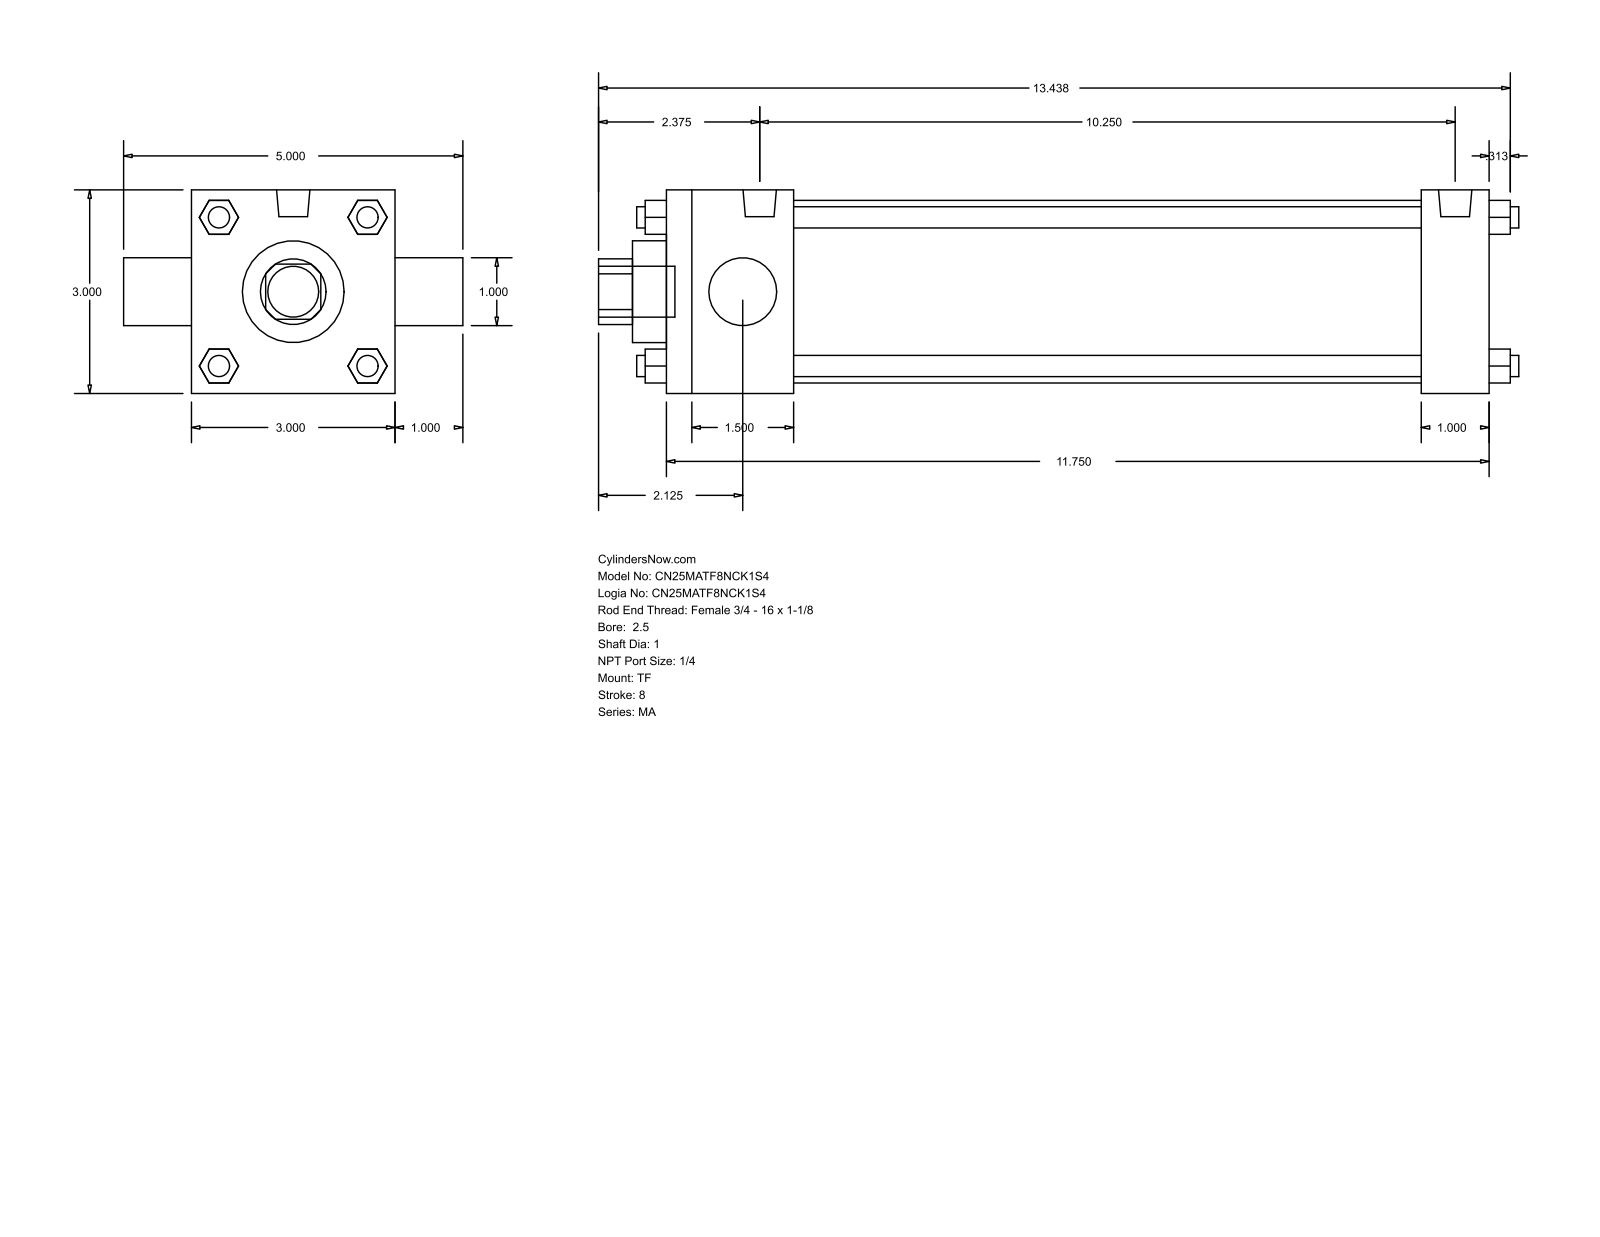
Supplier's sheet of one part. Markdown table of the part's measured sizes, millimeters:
| quantity | value |
| --- | --- |
| part name | MA_TF__0250_1 |
| STEP written by | GSSL Pune (CONFIG_CONTROL_DESIGN) |
| units | millimeters |
| bodies | 0 solids, 120 faces (92 planar, 28 cylindrical, 0 other) |
| overall size | 344.49 × 127 × 76.2 |
| round holes (diameter × count) | 25.4 × 2, 38.1 × 1, 68.33 × 1 |
| round bosses / shafts (diameter × count) | 7.94 × 7, 12.49 × 2, 19.05 × 1 |
| partial cylindrical surfaces (radius × count) | 12.29 × 1 |
| main face-to-face distances | 76.2, 307.98, 25.4, 12.7, 47.63, 282.58, 234.95, 260.35, 101.6, 27.81 |
